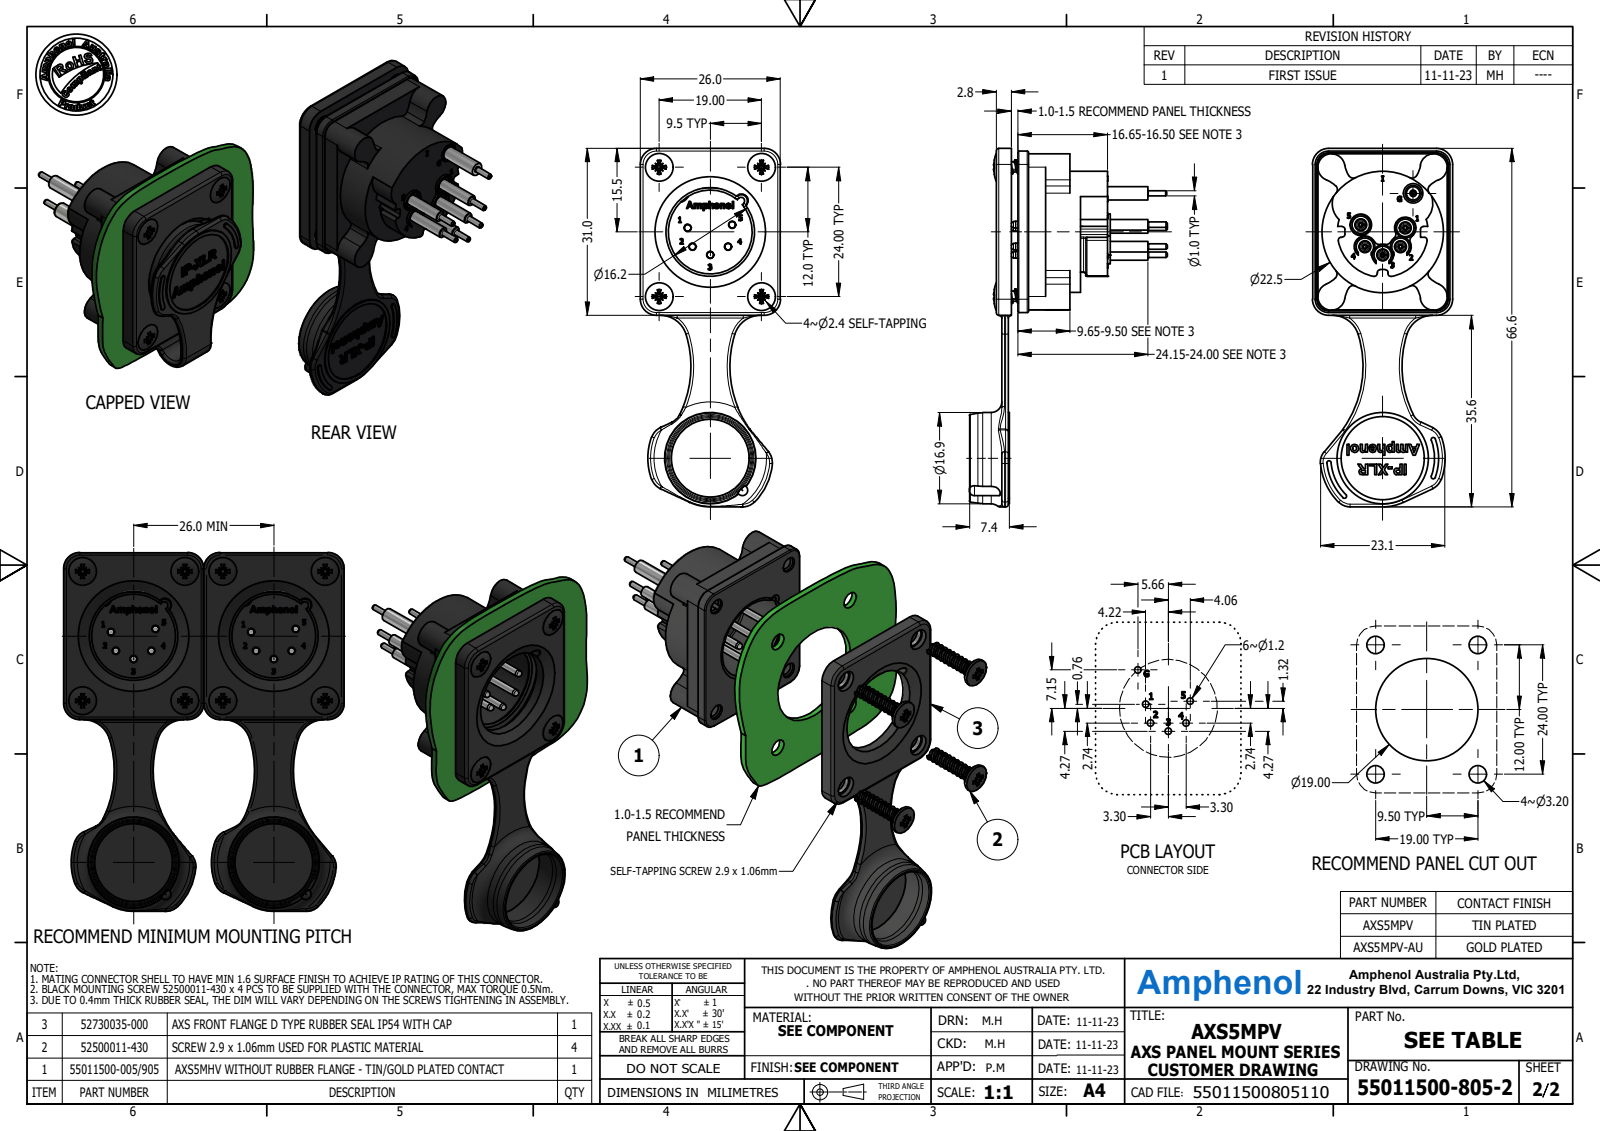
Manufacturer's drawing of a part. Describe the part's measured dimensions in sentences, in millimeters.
The part is named "55011500-805". Its 3-D file was written by "Autodesk Inventor 2023 (AUTOMOTIVE_DESIGN)". It is 1 solid with 2143 faces: 551 planar, 464 cylindrical and 1128 other. Overall it measures 66.5 by 36.7 by 26 millimeters. Its volume is 8 490 cubic millimeters and its surface area 8 755 square millimeters. Round holes: 5 of diameter 1.3, 5 of diameter 2.2, 4 of diameter 2.4, 4 of diameter 3.4, 4 of diameter 4, 2 of diameter 3.2, 1 of diameter 2.6, 1 of diameter 3.6, 1 of diameter 14.4, 1 of diameter 15.4, 1 of diameter 15.5, 1 of diameter 16.2. Round bosses or shafts: 6 of diameter 1, 5 of diameter 2, 5 of diameter 1.3, 1 of diameter 22.5, 1 of diameter 17, 1 of diameter 16.9, 1 of diameter 4, 1 of diameter 3.4. Partial cylindrical surfaces (rounded edges, fillets, slot ends): 23 of radius 0.5, 16 of radius 1, 12 of radius 0.4, 12 of radius 1.1, 10 of radius 3, 10 of radius 5, 9 of radius 2, 8 of radius 0.3. The main face-to-face distances are 0.6, 1.6, 2.2, 2.3, 2.8, 4.4, 0.5, 3.4, 1.8, 1.2. The hole center spacings are 15.3, 4.3, 3.6, 4.3, 11.2, 12.2, 15.8, 16.
